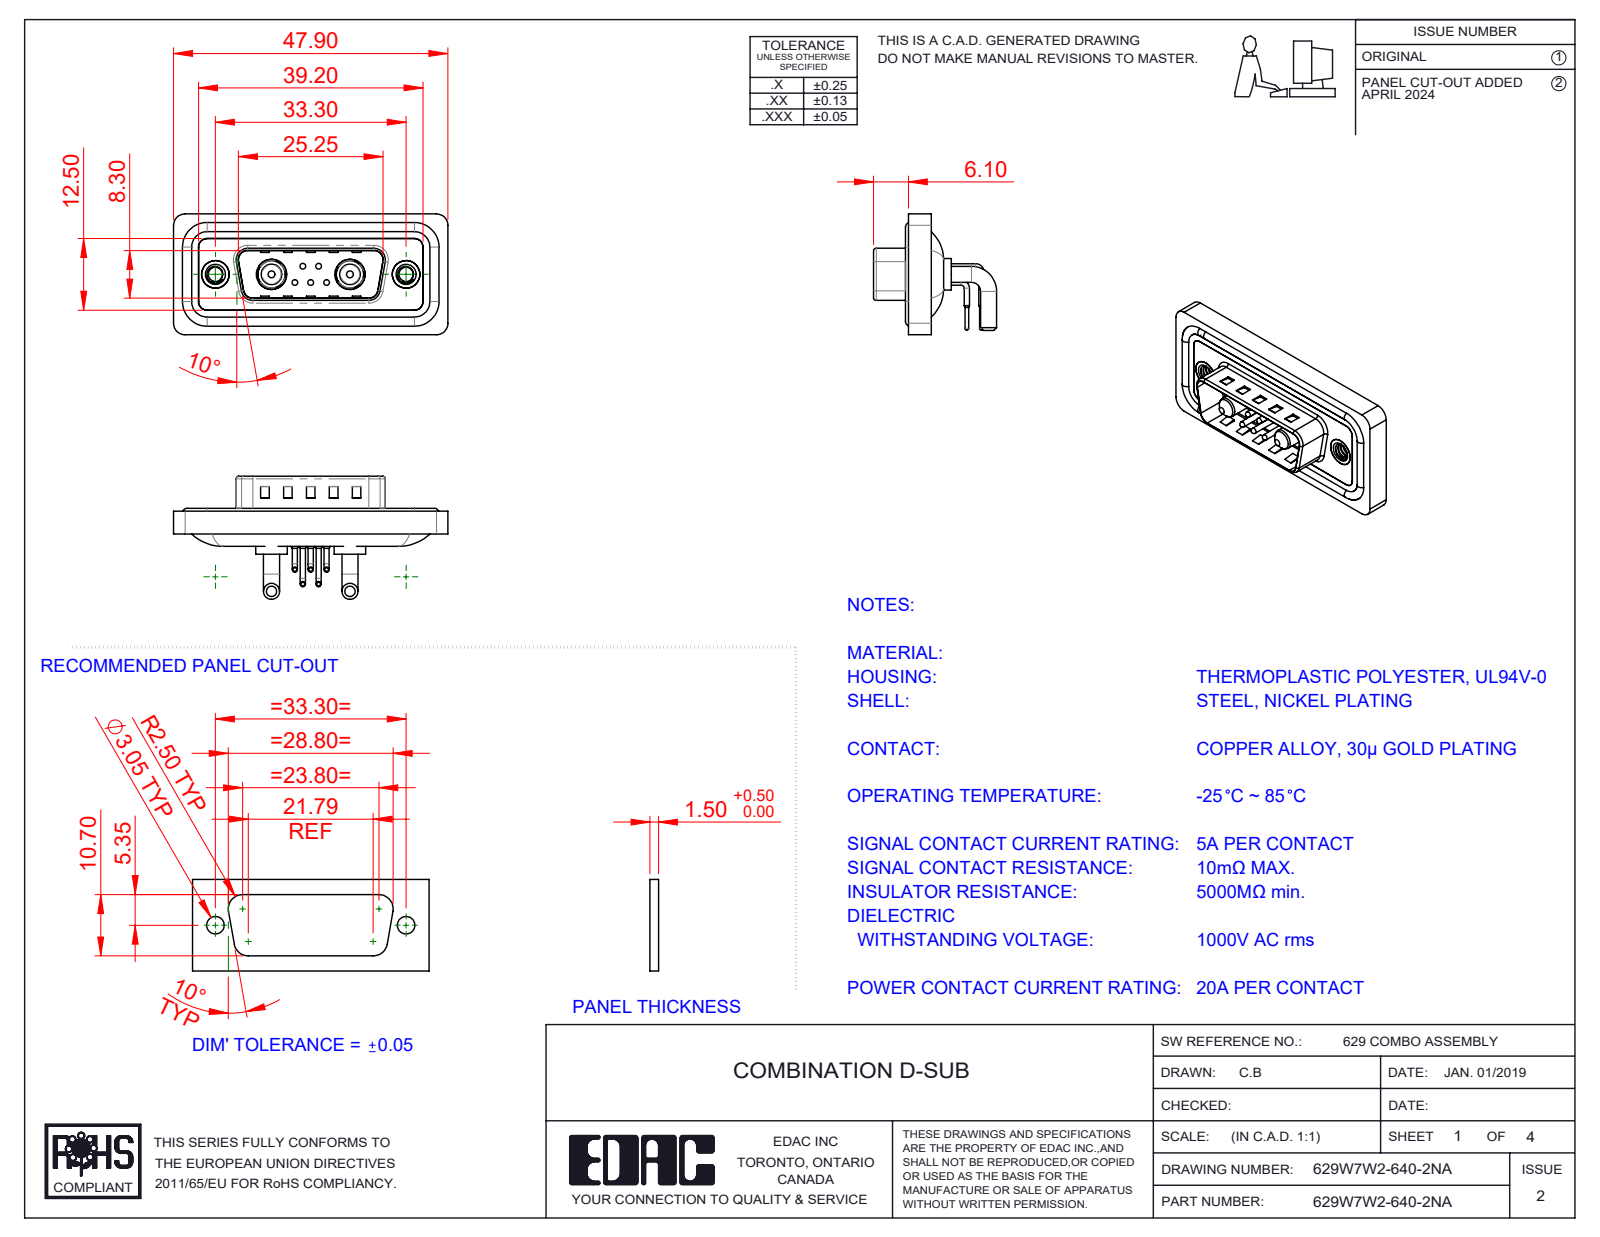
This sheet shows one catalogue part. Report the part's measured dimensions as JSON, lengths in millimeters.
{"part_name": "629Combo Threaded Rivet_A; 629Combo Contact Row 1; 629Combo Contact Row 2; Power Pin_20A RA (+5 more)", "step_written_by": "SolidWorks 2023 (CONFIG_CONTROL_DESIGN)", "units": "millimeters", "bodies": {"solids": 16, "faces": 1077, "planar": 517, "cylindrical": 404, "other": 156}, "overall_size": [47.9, 21.5, 21.1], "volume_mm3": 5684, "surface_area_mm2": 9144, "round_holes": [[0.75, 5], [1.6, 5], [2, 5], [2.5, 2], [4, 2], [4.8, 2], [4.85, 2], [5, 2], [5.3, 2]], "round_bosses_or_shafts": [[0.9, 10], [1.5, 5], [1, 5], [0.65, 5], [2.8, 4], [1.6, 4], [5.5, 2], [5.2, 2]], "partial_cylinders_radius": [[2, 20], [1.5, 18], [0.5, 8], [1.6, 8], [1.01, 5], [0.25, 4], [0.6, 4], [0.65, 4]], "face_to_face_distances": [0.4, 2.9, 0.8, 1.1, 2.1, 1.6, 2.5, 3.1, 4.5, 4.1], "hole_center_spacings": [3.16, 2.77, 9.8, 23.5, 4.31, 4.33, 5.03, 5.04]}
